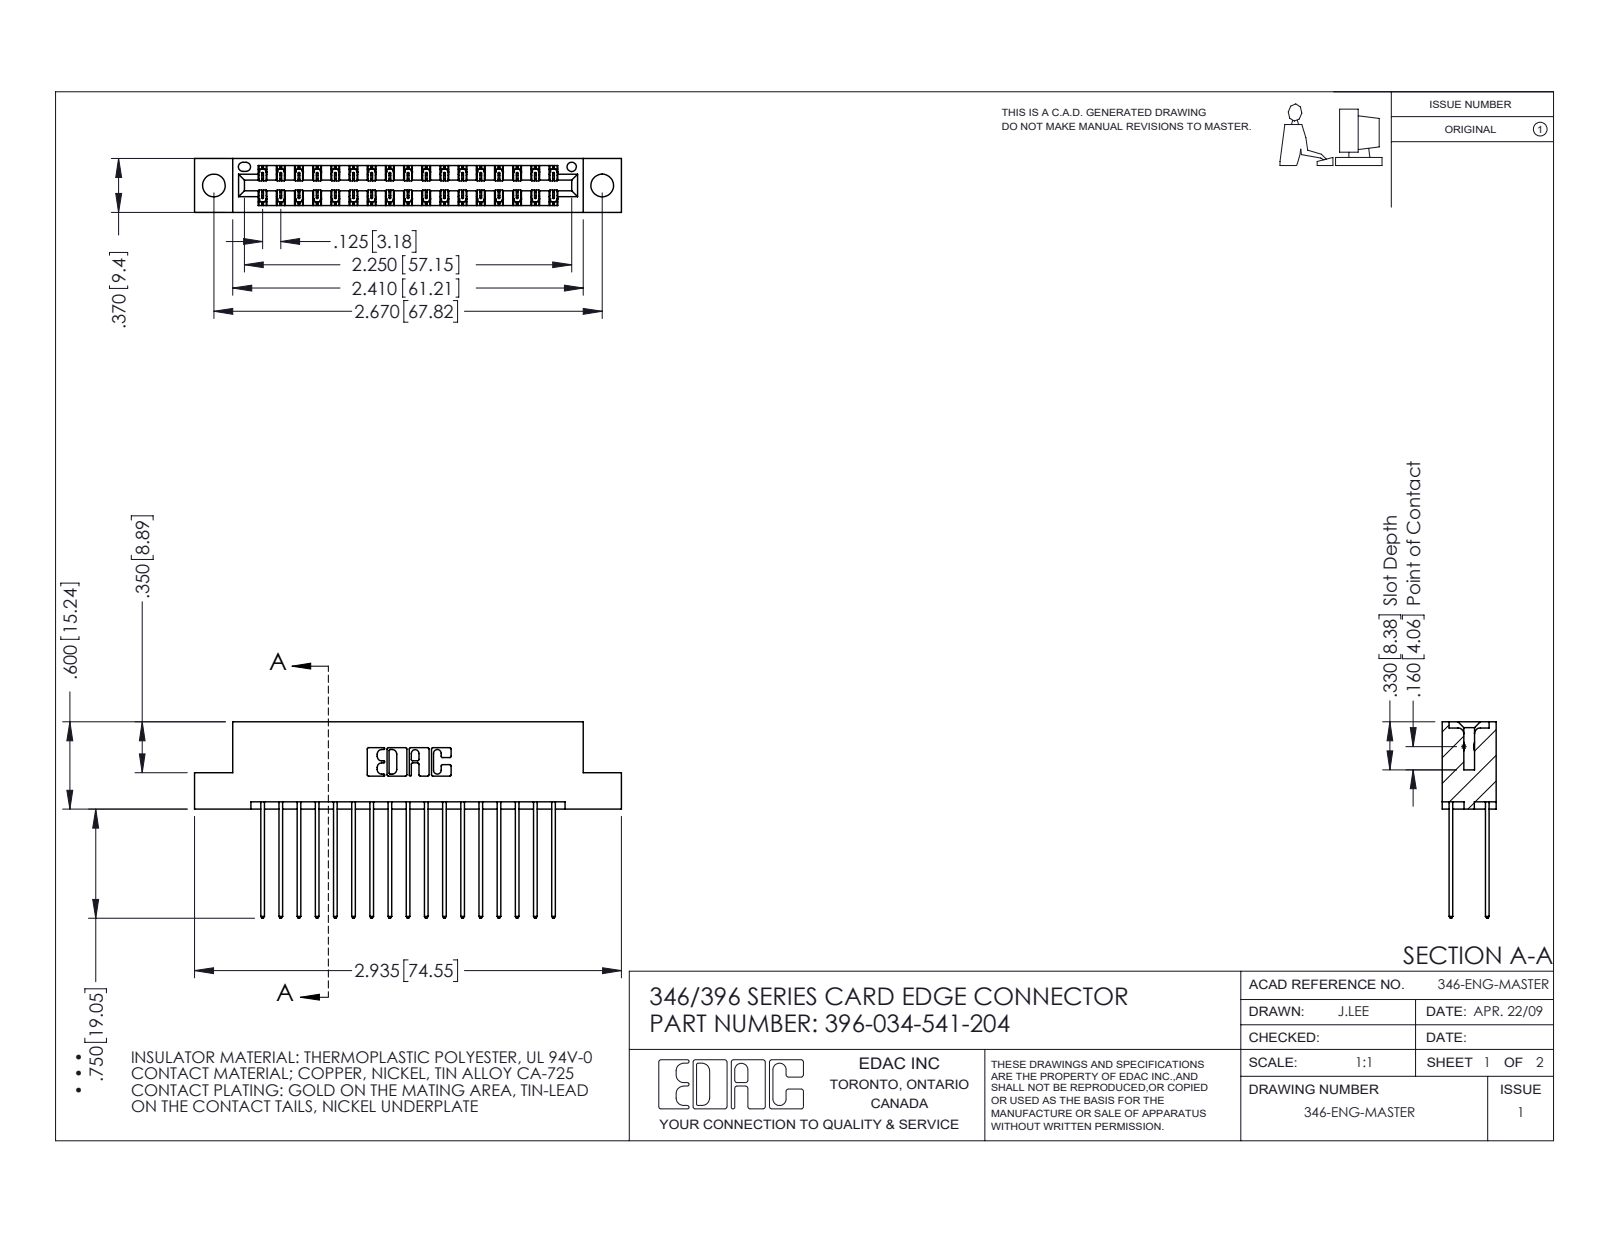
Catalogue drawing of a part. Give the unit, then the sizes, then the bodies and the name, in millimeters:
Units: millimetres
Overall size (bounding box): 74.5 × 34.3 × 9.4
Round holes (diameter × count): ⌀4 ×2, ⌀1.6 ×1
Partial cylindrical surfaces — rounded edges, fillets, slot ends (radius × count): R0.2 ×51, R0.3 ×34, R0.3 ×22, R0.2 ×6, R0.8 ×6, R0.7 ×3, R0.4 ×2, R0.6 ×2
Main face-to-face distances: 1.2, 8.2, 6.4, 1.8, 7.6, 0.6, 9.4, 7, 3.8, 5.6
Hole centre spacings: 6.2, 62.6, 67.8
Volume: 7 180 mm³ · Surface area: 10 230 mm²
Bodies: 35 solids, 1890 faces (1266 planar, 624 cylindrical, 0 other)
Part name (STEP PRODUCT): 396-034-541-204; 346 Part_Flush Mounting Lugs - 0.156 Dia-TH; 345-292-001_345-293-141
STEP written by: SolidWorks 2016 (CONFIG_CONTROL_DESIGN)
